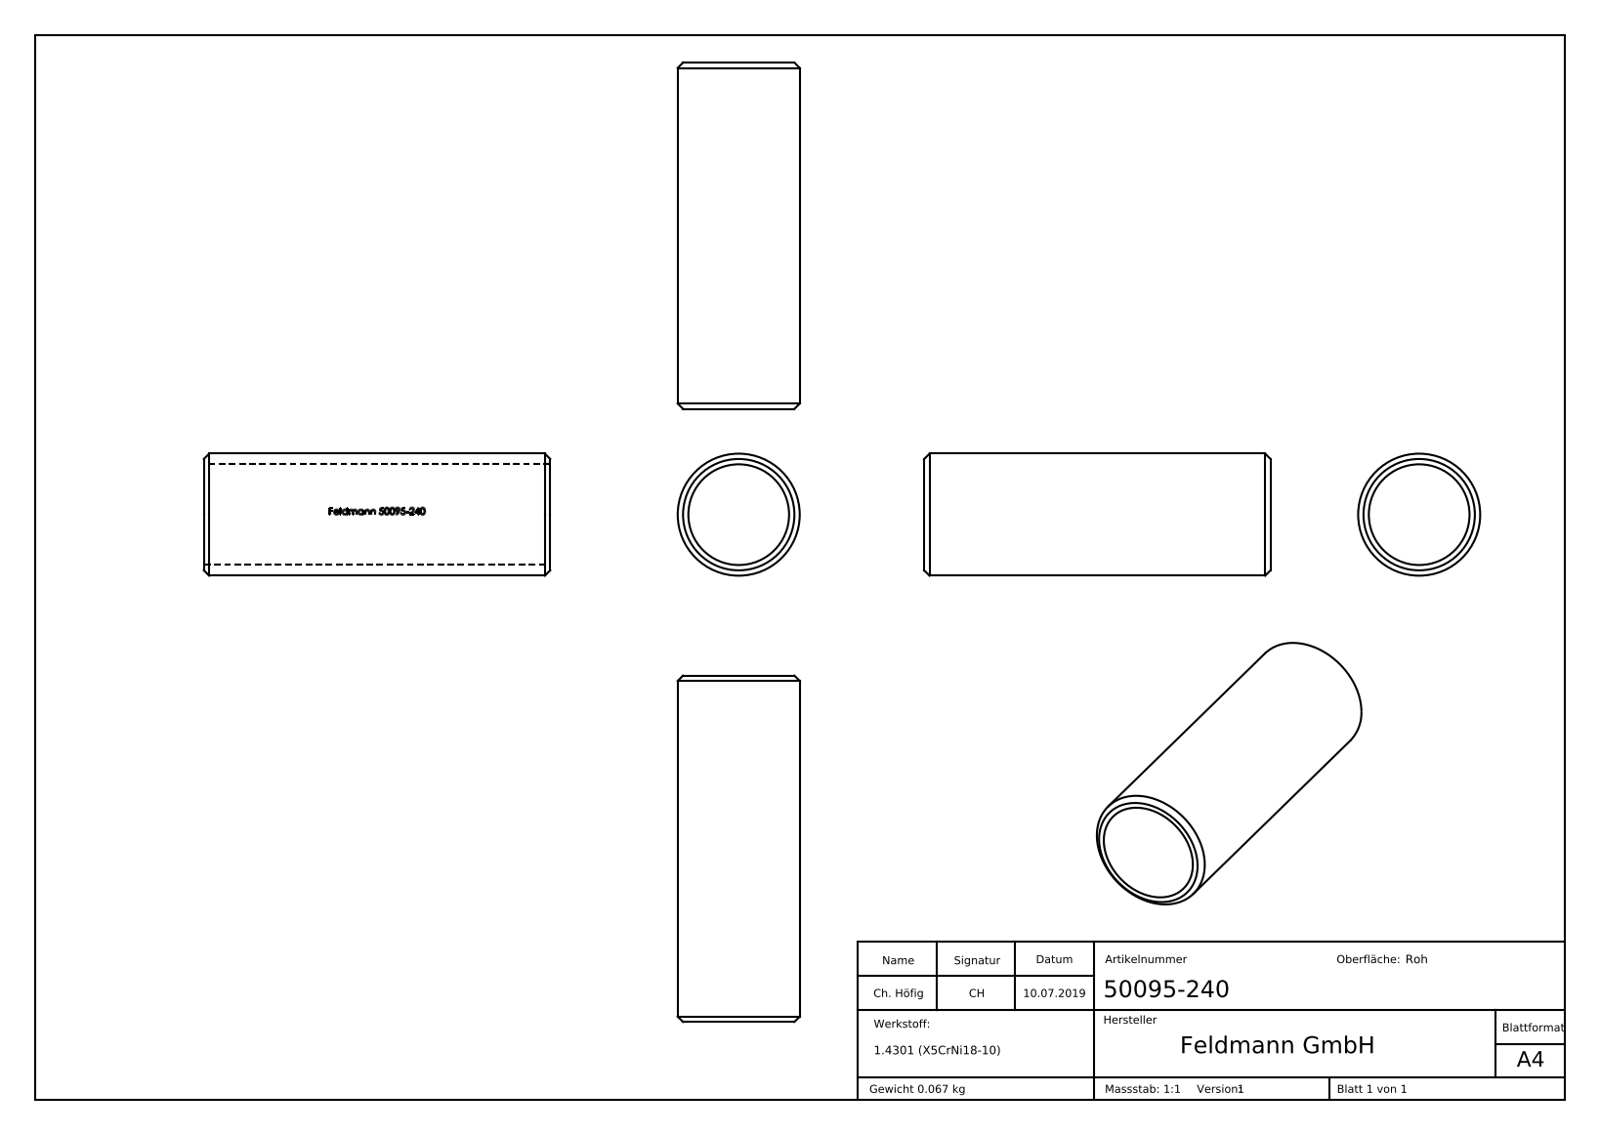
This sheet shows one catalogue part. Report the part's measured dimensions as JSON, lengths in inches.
{"part_name": "50095-240", "step_written_by": "SolidWorks 2015 (CONFIG_CONTROL_DESIGN)", "units": "inches", "bodies": {"solids": 1, "faces": 248, "planar": 94, "cylindrical": 44, "other": 110}, "overall_size": [2.559, 0.902, 0.902], "volume_in3": 0.517, "surface_area_in2": 13.52, "round_holes": [[0.744, 1]], "round_bosses_or_shafts": [[0.902, 1]], "partial_cylinders_radius": [[0.376, 1]], "face_to_face_distances": [2.559, 0.015, 0.117, 0.052, 0.576, 0.017, 0.044, 0.161, 0.05, 0.035]}
